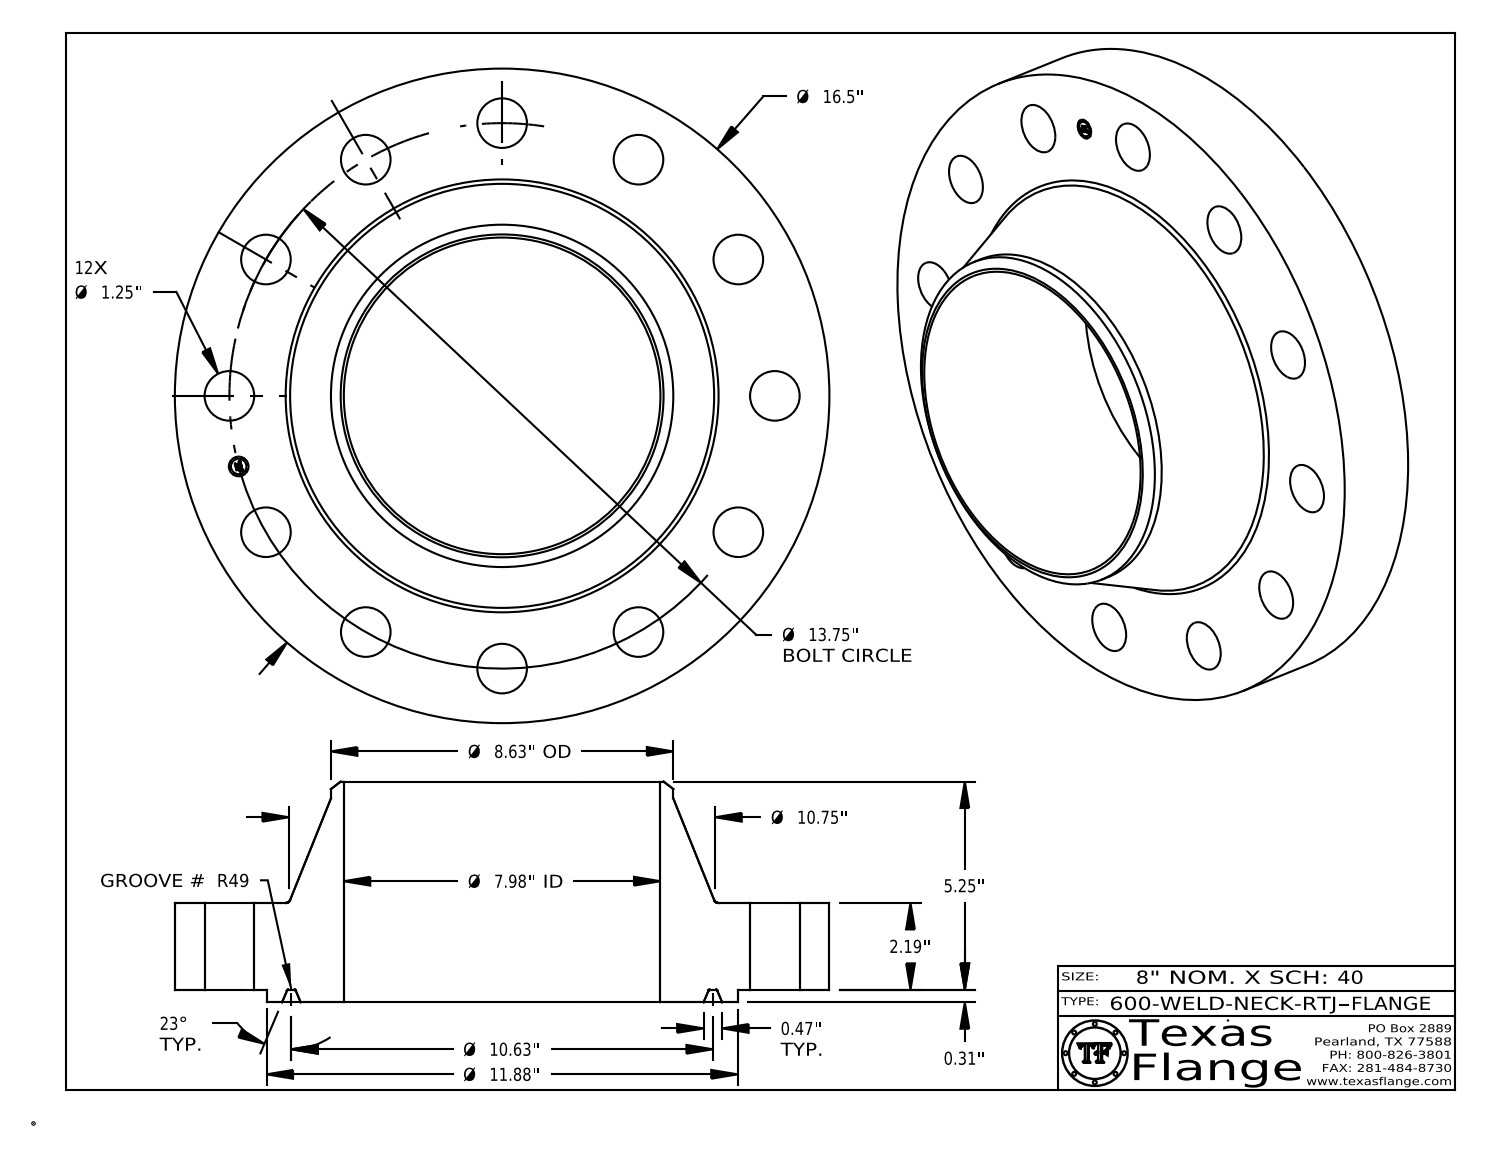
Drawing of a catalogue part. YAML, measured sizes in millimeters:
part_name: "600-WELD-NECK-RTJ"
step_written_by: "CATIA V5 STEP AP214 (AUTOMOTIVE_DESIGN)"
units: millimeters
bodies: {solids: 1, faces: 437, planar: 371, cylindrical: 52, other: 14}
overall_size: [419.1, 419.1, 141.3]
volume: 6691000
surface_area: 478300
round_holes:
  - {diameter: 31.8, count: 12}
  - {diameter: 12.6, count: 1}
  - {diameter: 202.7, count: 1}
round_bosses_or_shafts:
  - {diameter: 0.8, count: 8}
  - {diameter: 419.1, count: 1}
  - {diameter: 301.6, count: 1}
  - {diameter: 219.2, count: 1}
  - {diameter: 9.9, count: 1}
face_to_face_distances: [55.6, 8, 63.6, 141.3, 133.4, 77.7, 63.2, 55.2, 0.4, 78.1]
hole_center_spacings: [174.6, 174.6, 247, 302.5, 337.3, 90.4, 90.4, 349.3]
